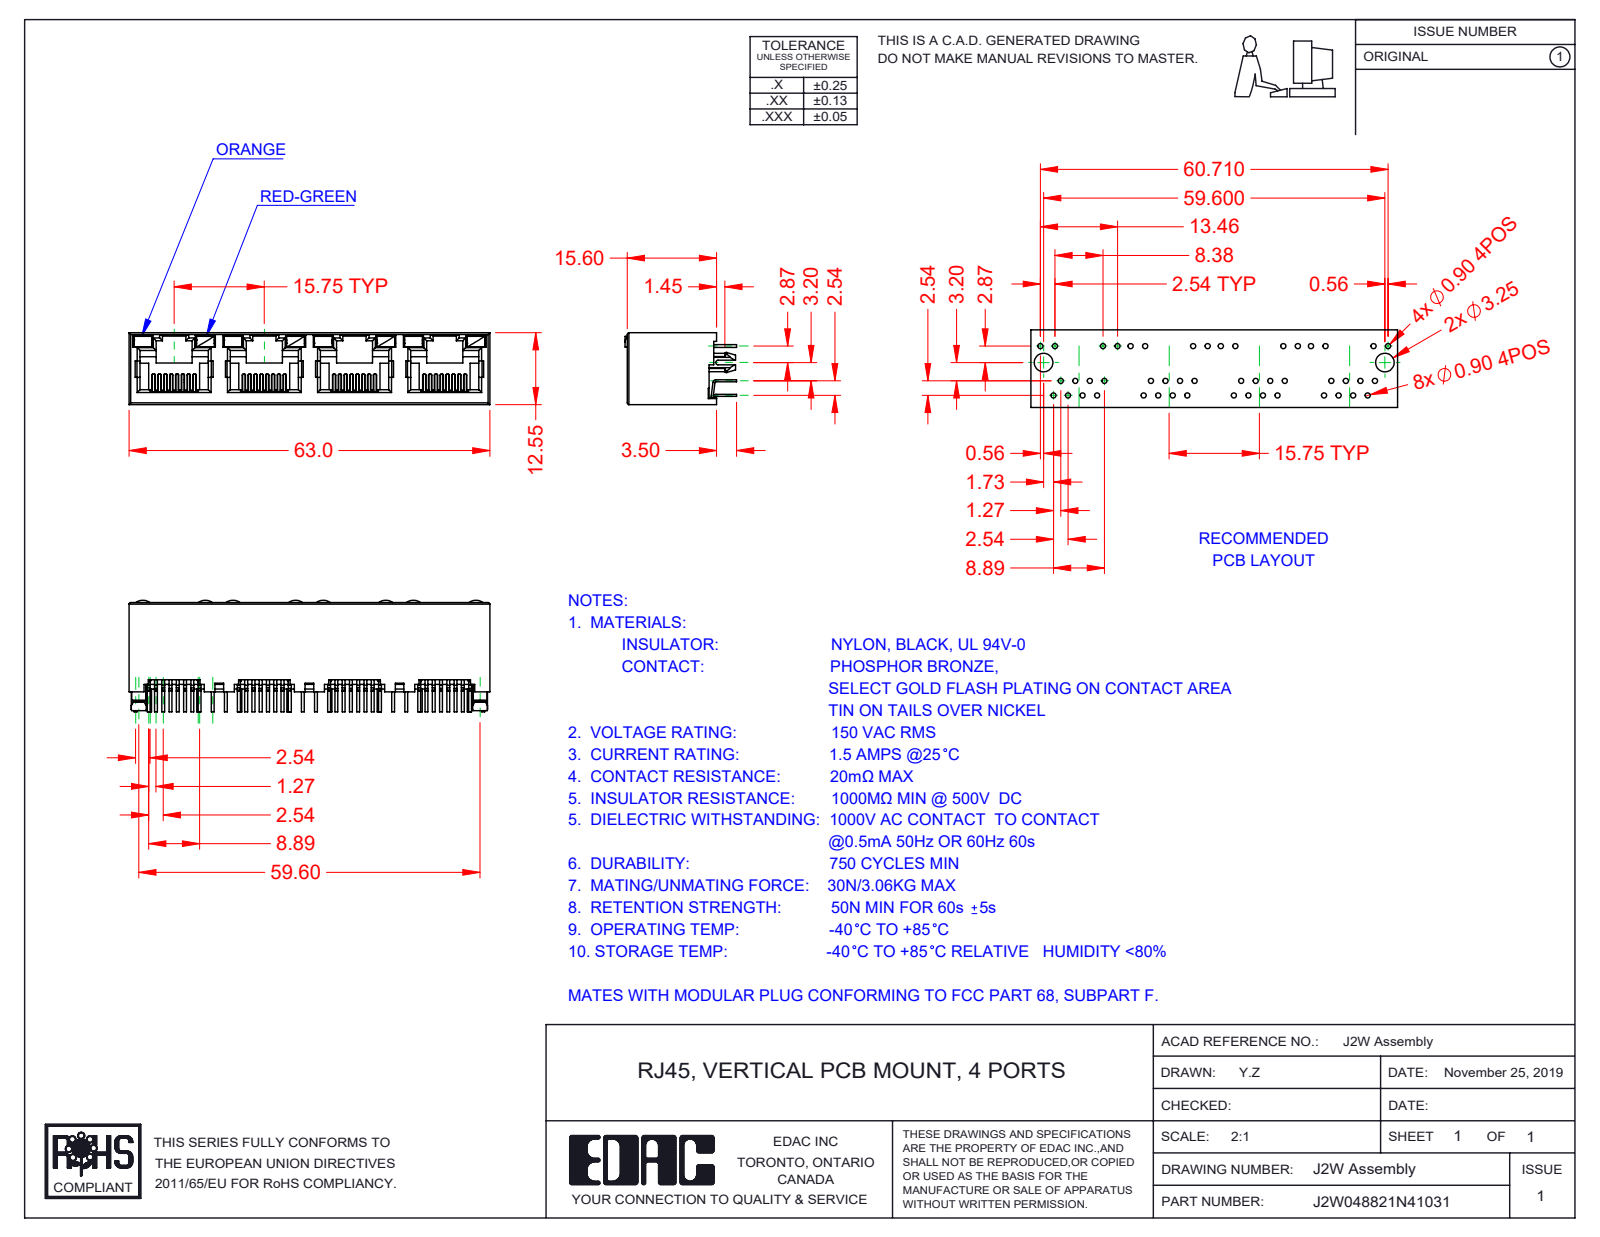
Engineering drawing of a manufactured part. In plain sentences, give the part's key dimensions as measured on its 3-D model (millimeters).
The part is named "2W Contact Lock; 2W Contacts; J2W048821N46131; 2W LED LH_4-Orange (+2 more)". Its 3-D file was written by "SolidWorks 2016 (CONFIG_CONTROL_DESIGN)". It is 45 solids with 3139 faces: 2600 planar, 481 cylindrical and 58 other. Overall it measures 63 by 19.5 by 12.55 millimeters. Its volume is 5 335 cubic millimeters and its surface area 13 144 square millimeters. Partial cylindrical surfaces (rounded edges, fillets, slot ends): 64 of radius 0.15, 29 of radius 0.2, 28 of radius 0.5, 14 of radius 0.3, 8 of radius 0.45, 8 of radius 2, 2 of radius 0.25, 2 of radius 1.5. The main face-to-face distances are 12.55, 11.9, 0.65, 15.75, 0.36, 1.5, 0.78, 0.6, 11.3, 31.5.
